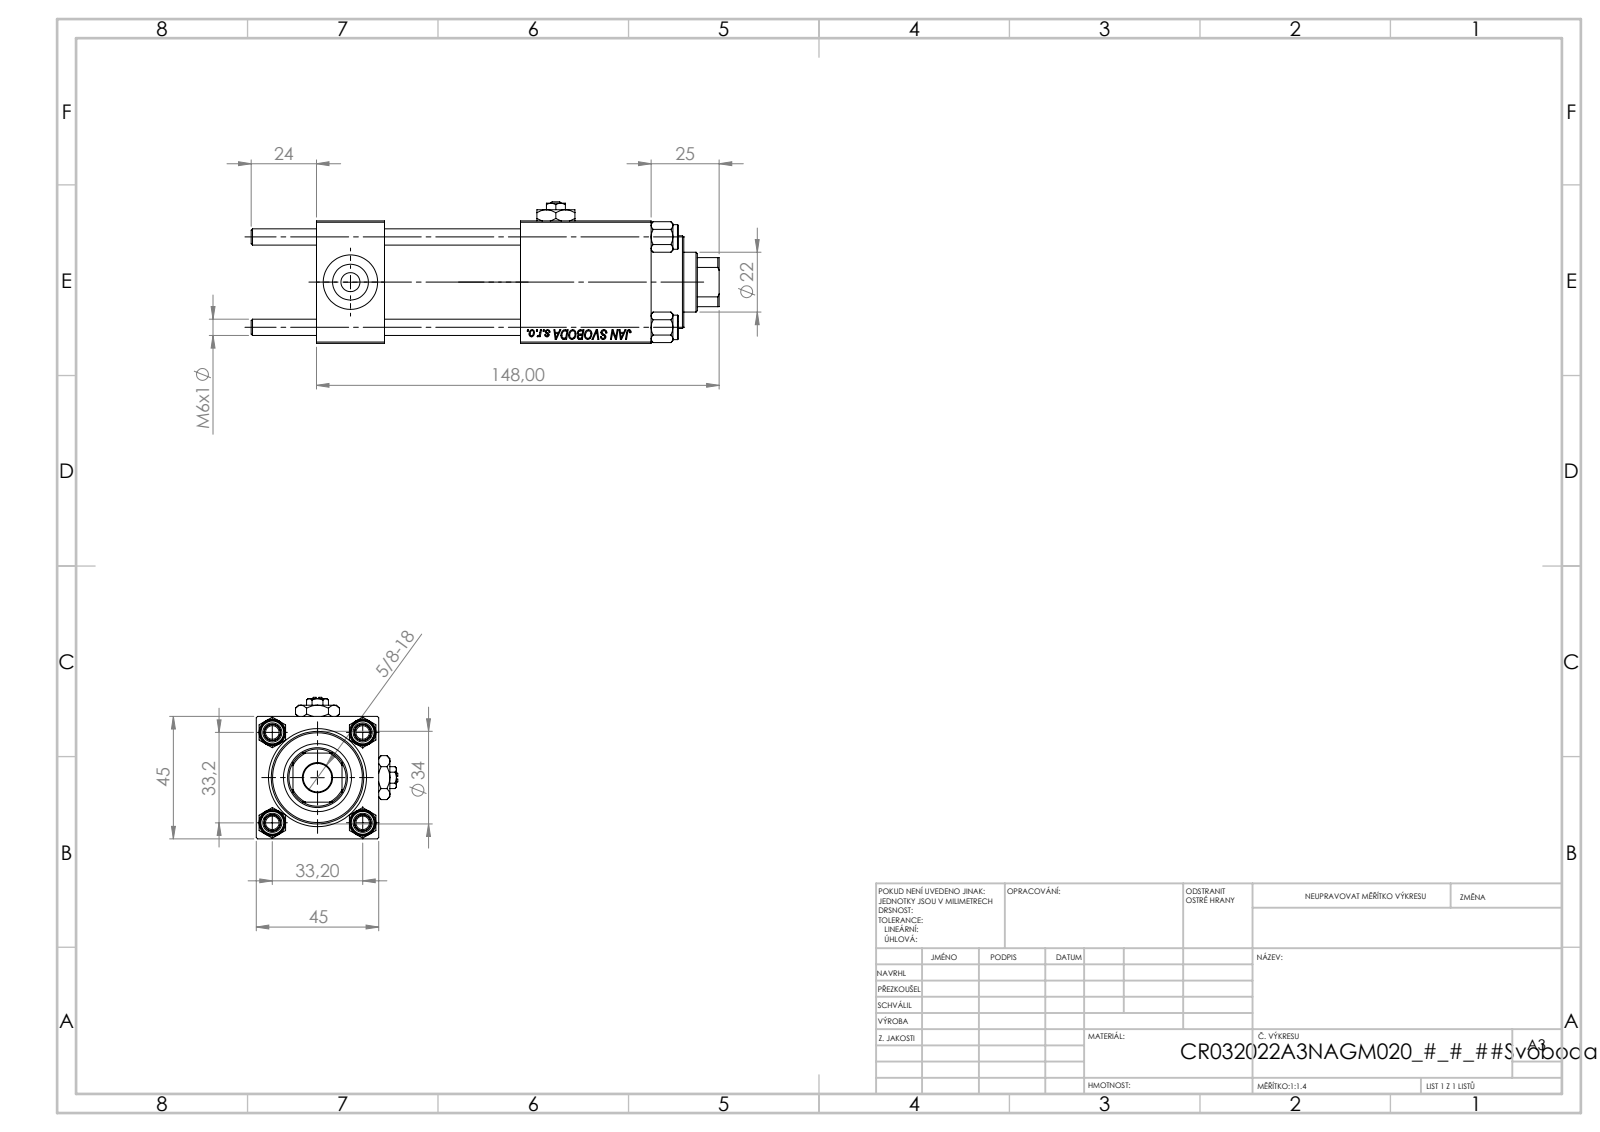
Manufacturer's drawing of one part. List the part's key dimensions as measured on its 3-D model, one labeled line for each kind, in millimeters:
Part name (STEP PRODUCT): V215CR_VCP; V215_VC_A; NUT_M5; V215CR_BODY_A (+2 more)
STEP written by: SolidWorks 2019 (CONFIG_CONTROL_DESIGN)
Units: millimetres
Bodies: 13 solids, 1232 faces (564 planar, 90 cylindrical, 578 other)
Overall size (bounding box): 172 × 52 × 52
Volume: 212 349 mm³ · Surface area: 78 934 mm²
Round holes (diameter × count): ⌀6 ×4, ⌀7 ×2, ⌀13.16 ×2, ⌀20 ×2, ⌀10.5 ×1, ⌀13 ×1, ⌀22 ×1, ⌀24 ×1, ⌀25 ×1, ⌀32 ×1, ⌀33 ×1
Round bosses / shafts (diameter × count): ⌀9 ×4, ⌀38 ×1, ⌀34 ×1
Partial cylindrical surfaces — rounded edges, fillets, slot ends (radius × count): R10.5 ×1
Main face-to-face distances: 45, 25, 123, 50, 75, 98, 48, 44.8, 94.3, 69.3
Hole centre spacings: 23.48, 33.2, 46.95
